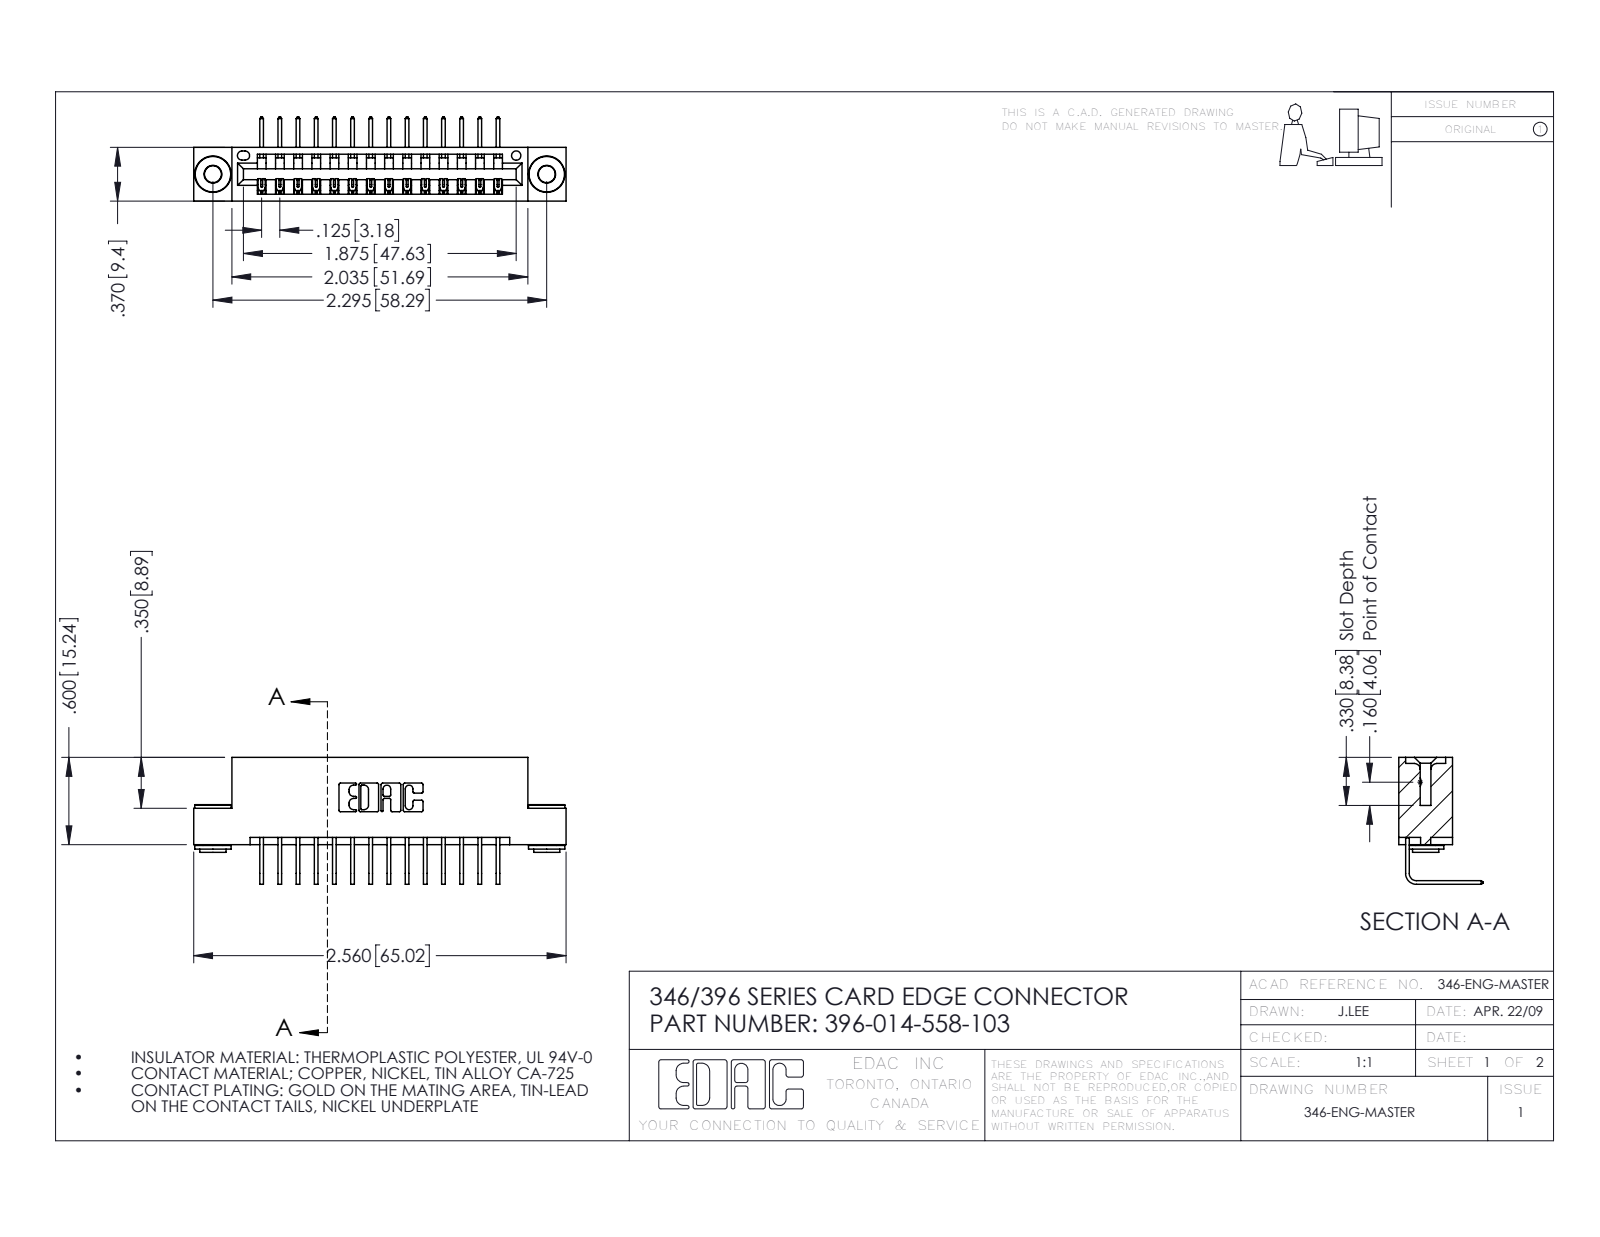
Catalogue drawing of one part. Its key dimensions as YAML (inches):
part_name: "345-292-001_558 Tail - 2; 345-250-002_345-250-002-102; 396-014-558-103; 346 Part_Flush Mounting Lugs - 0.156 Dia-TH"
step_written_by: "SolidWorks 2016 (CONFIG_CONTROL_DESIGN)"
units: inches
bodies: {solids: 17, faces: 1000, planar: 674, cylindrical: 318, other: 8}
overall_size: [2.56, 0.873, 0.58]
volume: 0.372
surface_area: 12.12
round_holes:
  - {diameter: 0.116, count: 2}
  - {diameter: 0.156, count: 2}
  - {diameter: 0.064, count: 1}
round_bosses_or_shafts:
  - {diameter: 0.25, count: 2}
  - {diameter: 0.18, count: 2}
  - {diameter: 0.136, count: 2}
partial_cylinders:
  - {radius: 0.006, count: 28}
  - {radius: 0.01, count: 22}
  - {radius: 0.007, count: 6}
  - {radius: 0.031, count: 6}
  - {radius: 0.026, count: 3}
  - {radius: 0.031, count: 2}
  - {radius: 0.04, count: 2}
  - {radius: 0.014, count: 1}
face_to_face_distances: [0.25, 0.322, 0.048, 0.37, 0.025, 0.298, 0.072, 0.148, 0.222, 0.1]
hole_center_spacings: [0.246, 2.089, 2.295]
